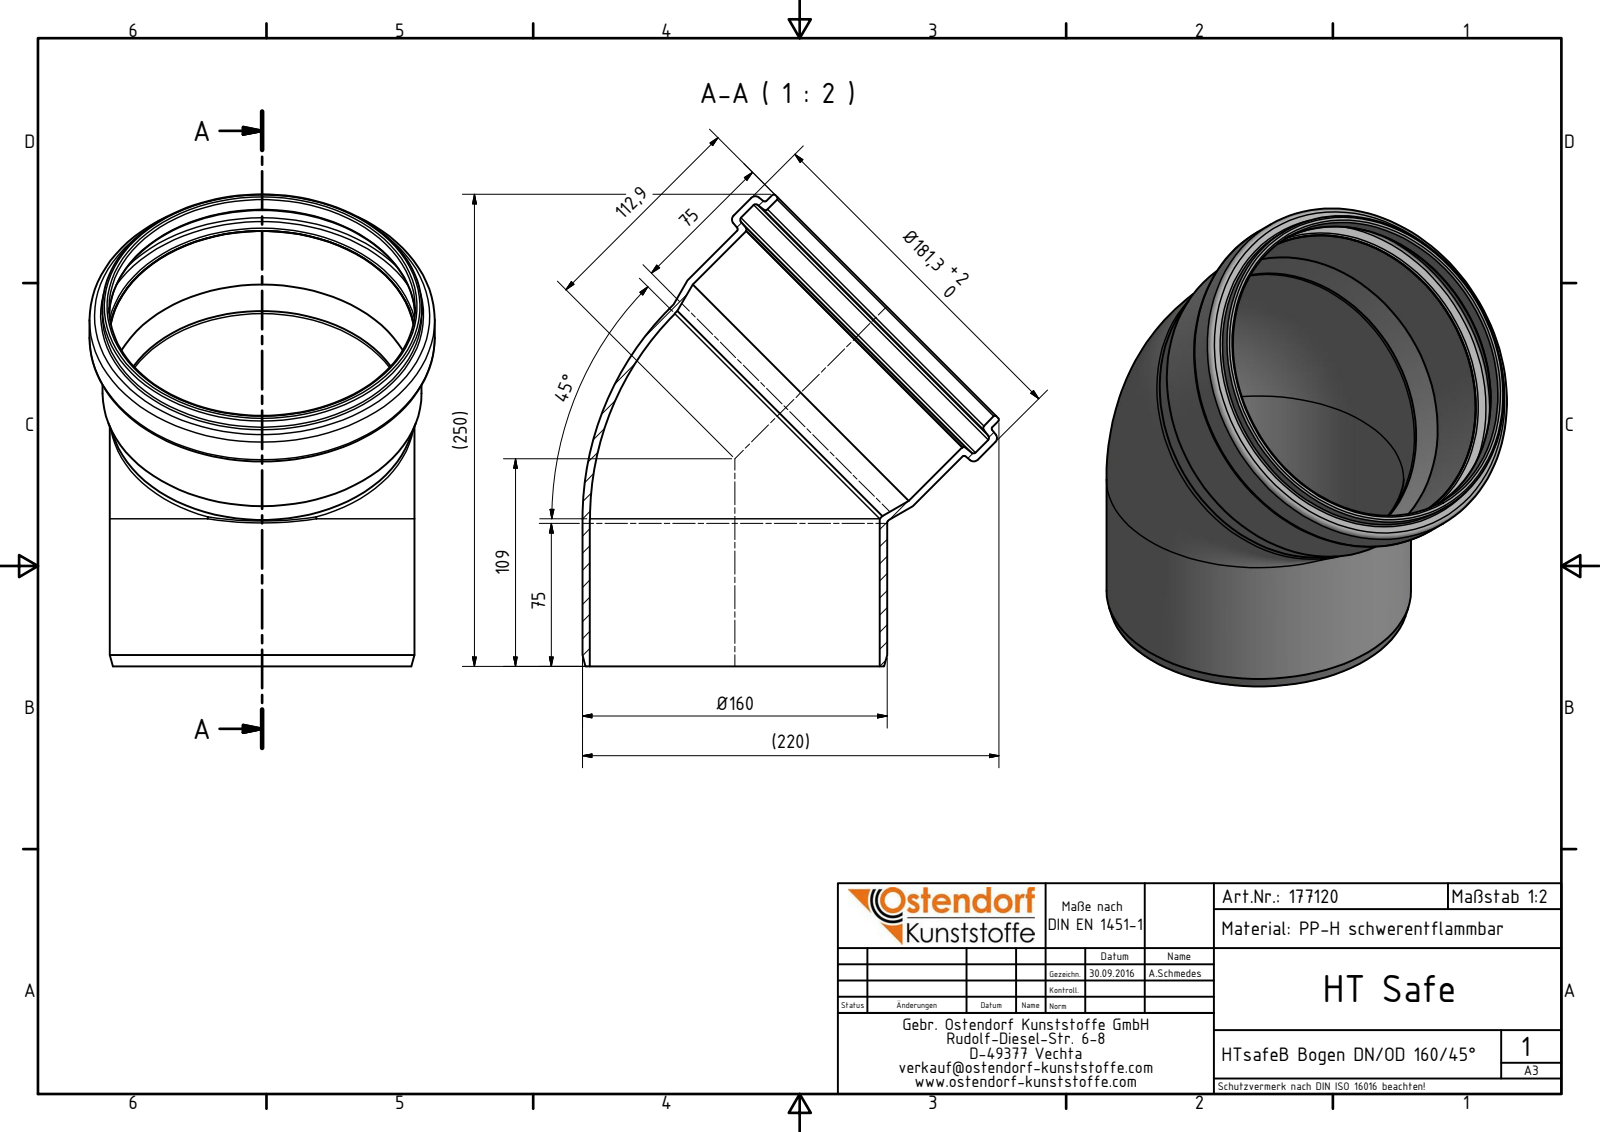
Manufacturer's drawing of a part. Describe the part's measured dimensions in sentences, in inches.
The part is named "177120 HTsafeB DN_OD 160_45°". Its 3-D file was written by "Autodesk Inventor 2016 (AUTOMOTIVE_DESIGN)". It is 1 solid with 35 faces: 4 planar, 11 cylindrical and 20 other. Overall it measures 9.754 by 8.612 by 7.138 inches. Its volume is 26.25 cubic inches and its surface area 361.5 square inches. Round holes: 2 of diameter 5.993, 1 of diameter 6.319, 1 of diameter 6.331, 1 of diameter 6.862. Round bosses or shafts: 2 of diameter 6.299, 1 of diameter 7.138, 1 of diameter 6.606, 1 of diameter 6.594. The main face-to-face distances are 0.953, 2.172, 3.125.
